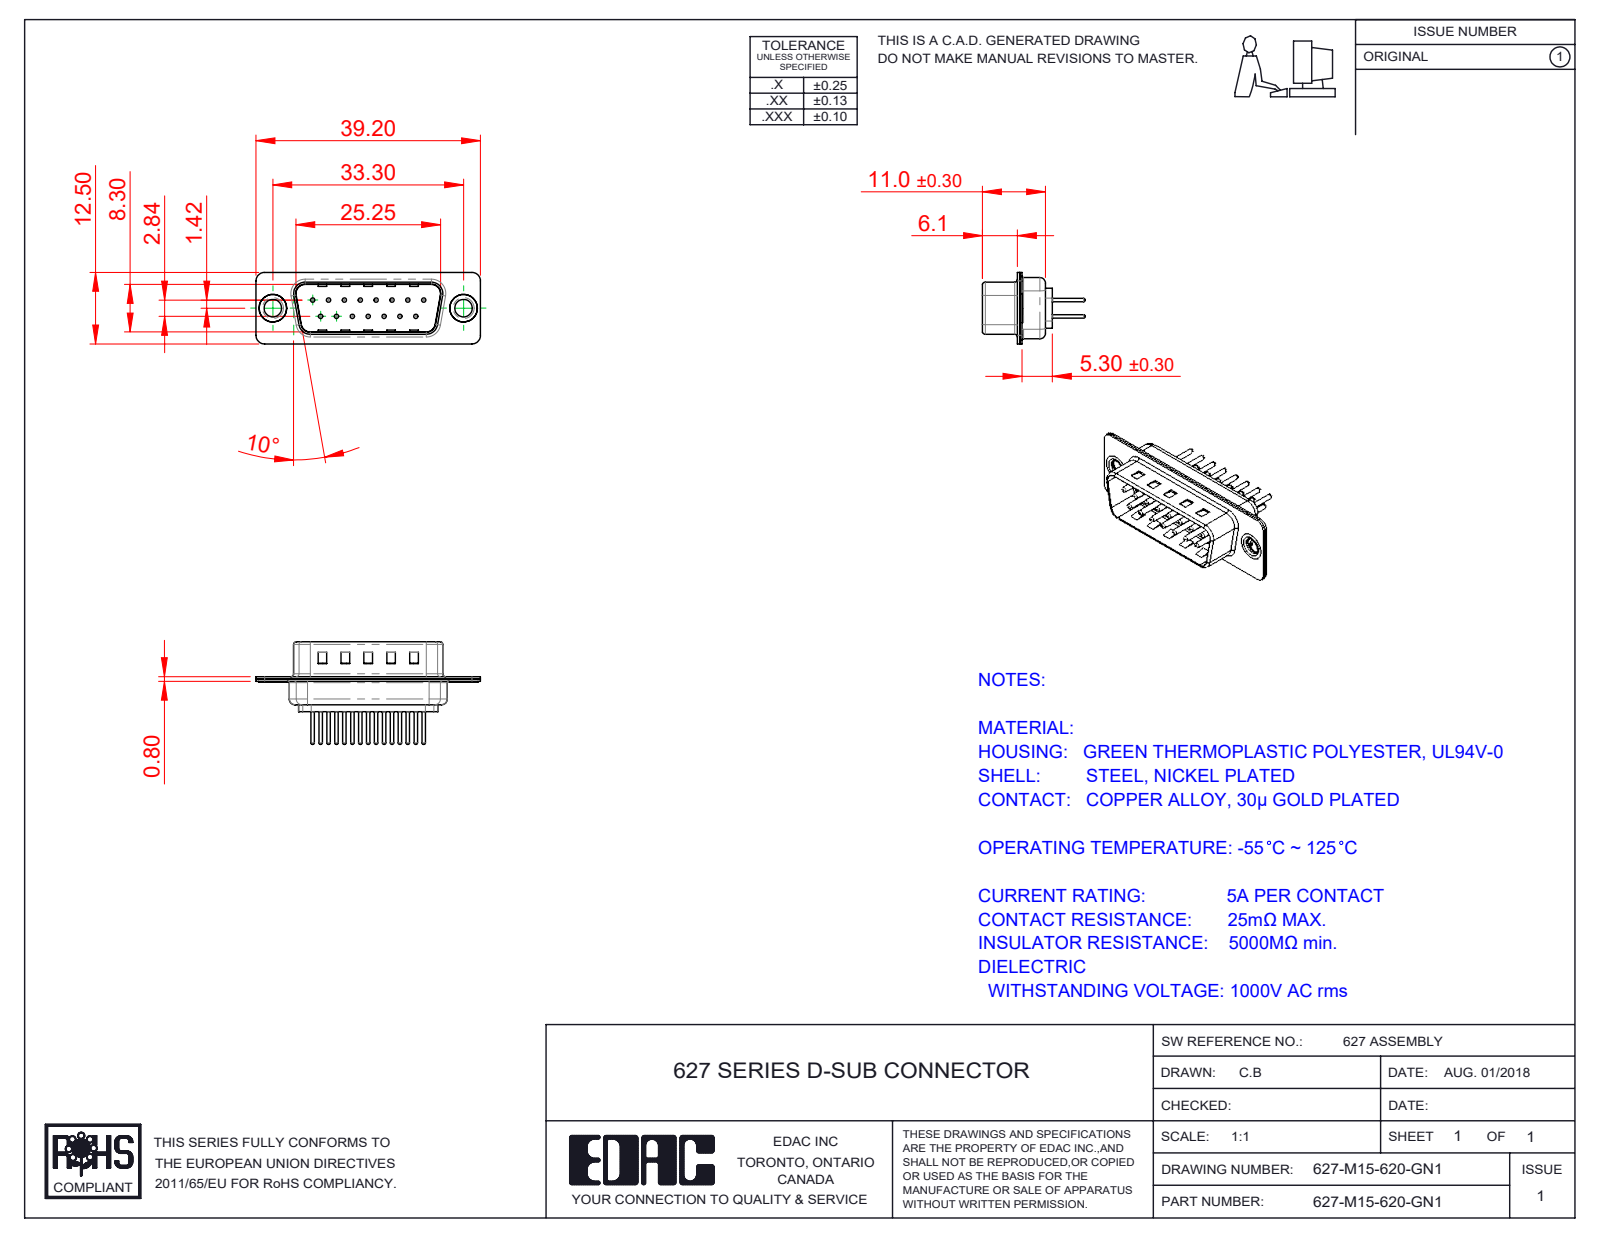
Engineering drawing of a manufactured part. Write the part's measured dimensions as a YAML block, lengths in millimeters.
part_name: "627M Contact Row 1_20; 627M Shell Front_15 Contacts; 627M Housing_15 Contacts; 627M Shell Rear_15 Contacts (+3 more)"
step_written_by: "SolidWorks 2020 (CONFIG_CONTROL_DESIGN)"
units: millimeters
bodies: {solids: 20, faces: 869, planar: 244, cylindrical: 327, other: 298}
overall_size: [39.2, 17.9, 12.5]
volume: 1765
surface_area: 4663
round_holes:
  - {diameter: 0.75, count: 15}
  - {diameter: 1.6, count: 15}
  - {diameter: 2, count: 15}
  - {diameter: 3.05, count: 2}
  - {diameter: 4, count: 2}
  - {diameter: 4.8, count: 2}
round_bosses_or_shafts:
  - {diameter: 1.5, count: 15}
  - {diameter: 0.6, count: 15}
  - {diameter: 5, count: 2}
  - {diameter: 4.9, count: 2}
  - {diameter: 3.55, count: 2}
partial_cylinders:
  - {radius: 1.5, count: 16}
  - {radius: 2, count: 12}
  - {radius: 0.5, count: 8}
  - {radius: 1.6, count: 8}
  - {radius: 0.25, count: 4}
  - {radius: 0.6, count: 4}
  - {radius: 0.65, count: 4}
  - {radius: 0.9, count: 4}
face_to_face_distances: [0.4, 0.8, 9.5, 9.1, 8.7, 9.9, 1.2, 6.1, 5.7, 5.3]
hole_center_spacings: [3.16, 2.77, 5.54, 8.31, 11.08, 5.03, 5.04, 7.48]
